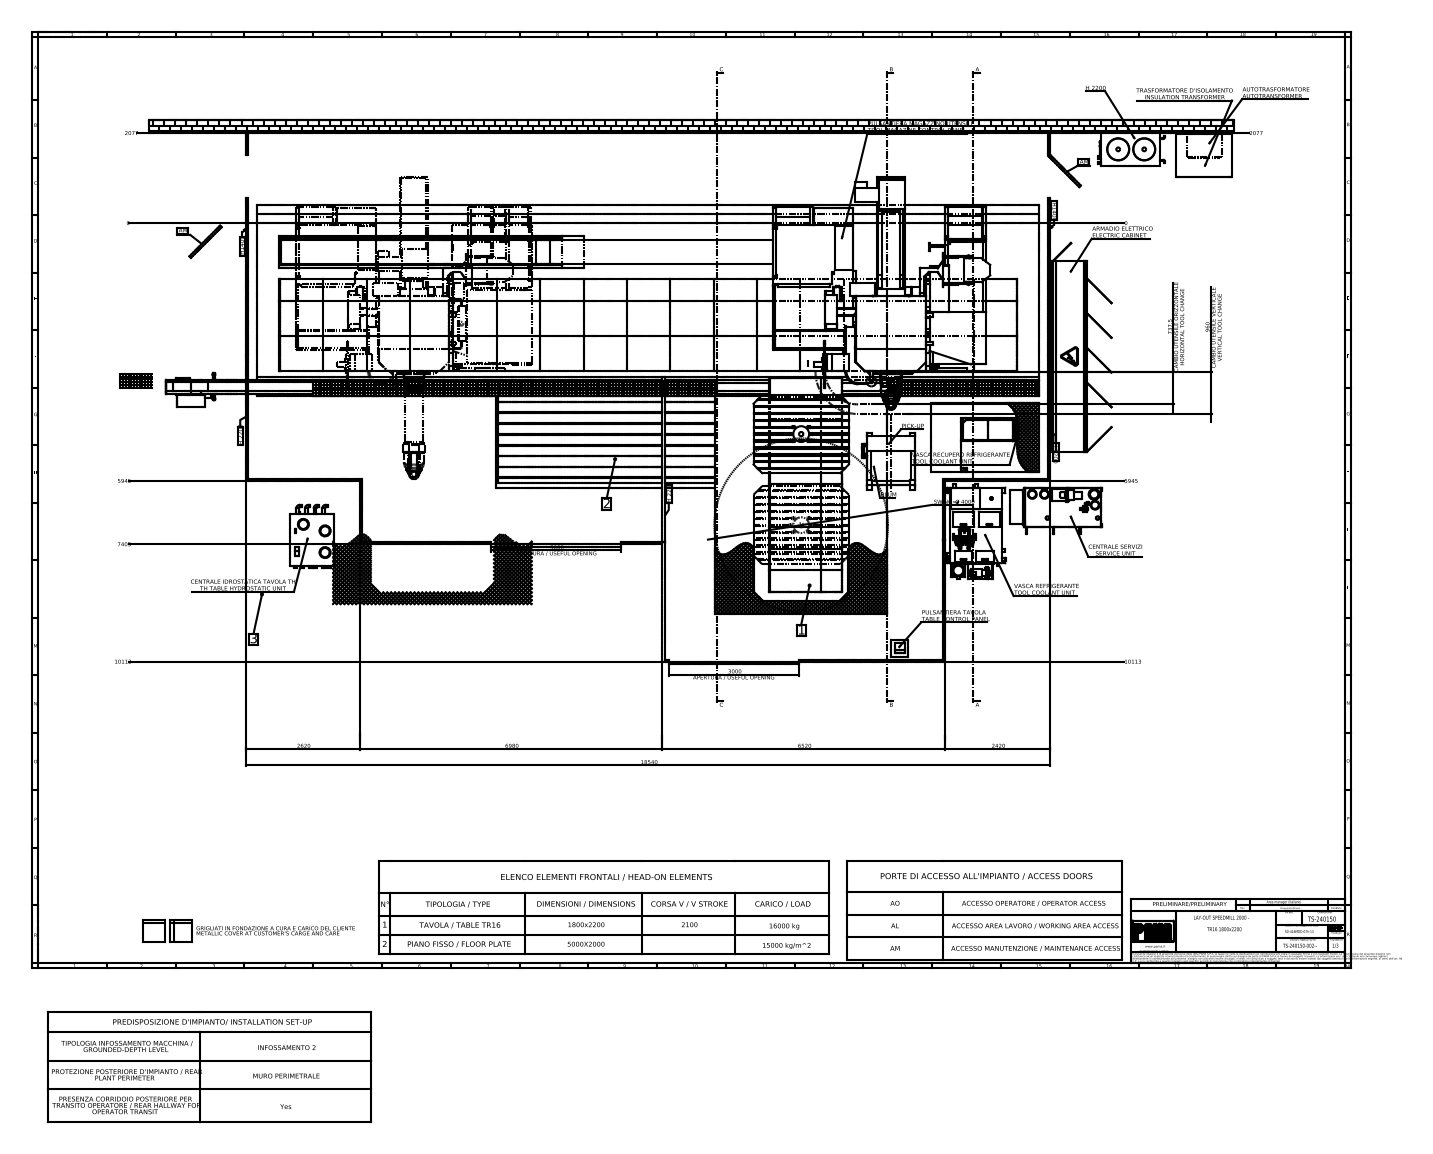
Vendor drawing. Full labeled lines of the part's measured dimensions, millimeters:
Part name (STEP PRODUCT): S001725_DRW6 (A = 0°); S003182_Lato PO - Inf. 2-3; S001726_SPEEDMILL 2000-3000; S002726_ATC con utensili orizzontali (+8 more)
STEP written by: SolidWorks 2023 (AUTOMOTIVE_DESIGN)
Units: millimetres
Bodies: 457 solids, 7689 faces (5373 planar, 1650 cylindrical, 666 other)
Overall size (bounding box): 25040 × 15440 × 9400
Volume: 782 700 000 000 mm³ · Surface area: 2 403 000 000 mm²
Round holes (diameter × count): ⌀35 ×122, ⌀69.6 ×63, ⌀13 ×8, ⌀14 ×8, ⌀8 ×6, ⌀32 ×6, ⌀12.5 ×4, ⌀50 ×3, ⌀56.66 ×3, ⌀4.2 ×2, ⌀19 ×2, ⌀30 ×2
Round bosses / shafts (diameter × count): ⌀20 ×14, ⌀9 ×10, ⌀30 ×8, ⌀66.3 ×7, ⌀60 ×7, ⌀35 ×6, ⌀200 ×4, ⌀170 ×4
Partial cylindrical surfaces — rounded edges, fillets, slot ends (radius × count): R5 ×166, R15 ×46, R6 ×41, R10 ×27, R35 ×26, R3 ×20, R20 ×20, R8 ×18
Main face-to-face distances: 2000, 300, 50, 1340, 660, 15440, 15140, 100, 25040, 2708
Hole centre spacings: 250, 500, 750, 1000, 1250, 1500, 1750, 2000
